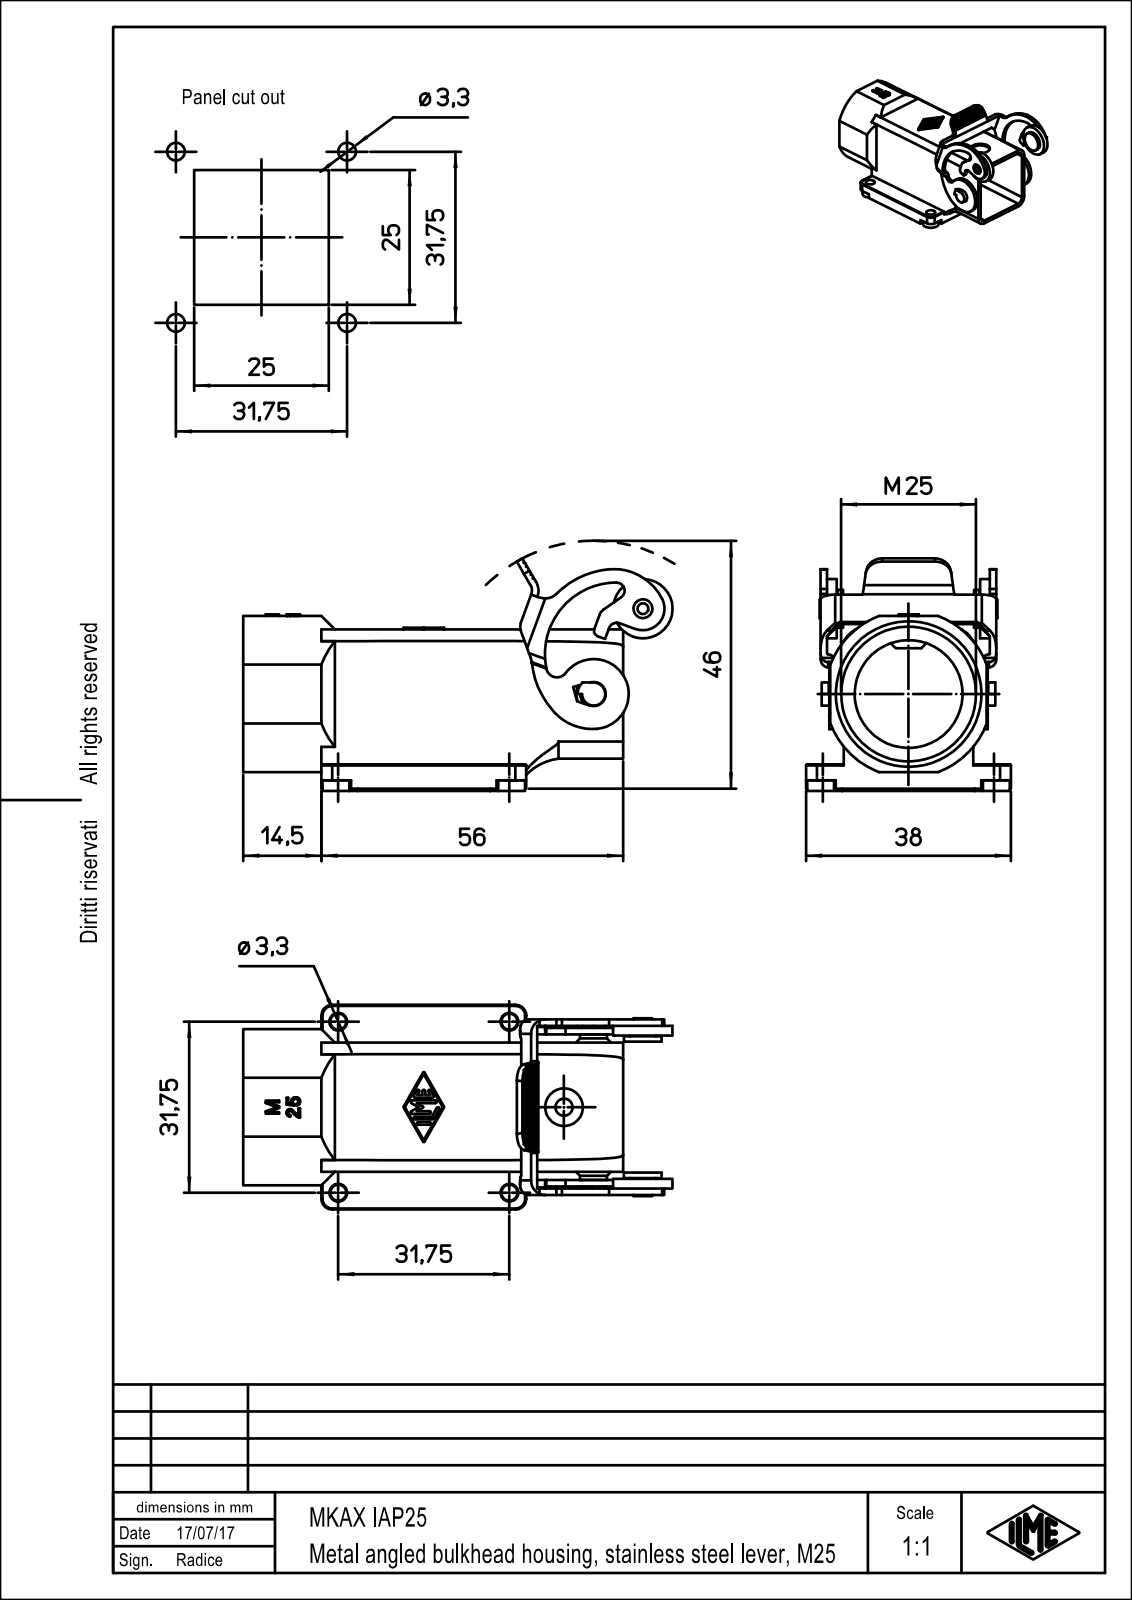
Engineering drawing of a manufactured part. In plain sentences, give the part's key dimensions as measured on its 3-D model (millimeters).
The part is named "MKAX_IAP25". Its 3-D file was written by "PTC Creo Elements/Direct Modeling 19.0E 27-Jun-2016 (C) Parametric Technology GmbH (AUTOMOTIVE_DESIGN)". It is 1 solid with 514 faces: 319 planar, 174 cylindrical and 21 other. Overall it measures 79.63 by 43.2 by 38 millimeters. Its volume is 16 087 cubic millimeters and its surface area 18 267 square millimeters. Round holes: 4 of diameter 3, 4 of diameter 3.3, 1 of diameter 2, 1 of diameter 3.2, 1 of diameter 5, 1 of diameter 7, 1 of diameter 20, 1 of diameter 25. Round bosses or shafts: 1 of diameter 11, 1 of diameter 7, 1 of diameter 5, 1 of diameter 4.8, 1 of diameter 4.3, 1 of diameter 3.5. Partial cylindrical surfaces (rounded edges, fillets, slot ends): 20 of radius 2, 16 of radius 0.2, 15 of radius 0.25, 11 of radius 3.2, 5 of radius 3, 4 of radius 1.4, 4 of radius 2.9, 3 of radius 0.12. The main face-to-face distances are 1.2, 22.8, 24, 21.6, 2.7, 4.3, 29.8, 2.5, 5.5, 3.9. The hole center spacings are 31.75, 44.79, 44.9, 18.83, 18.84.
